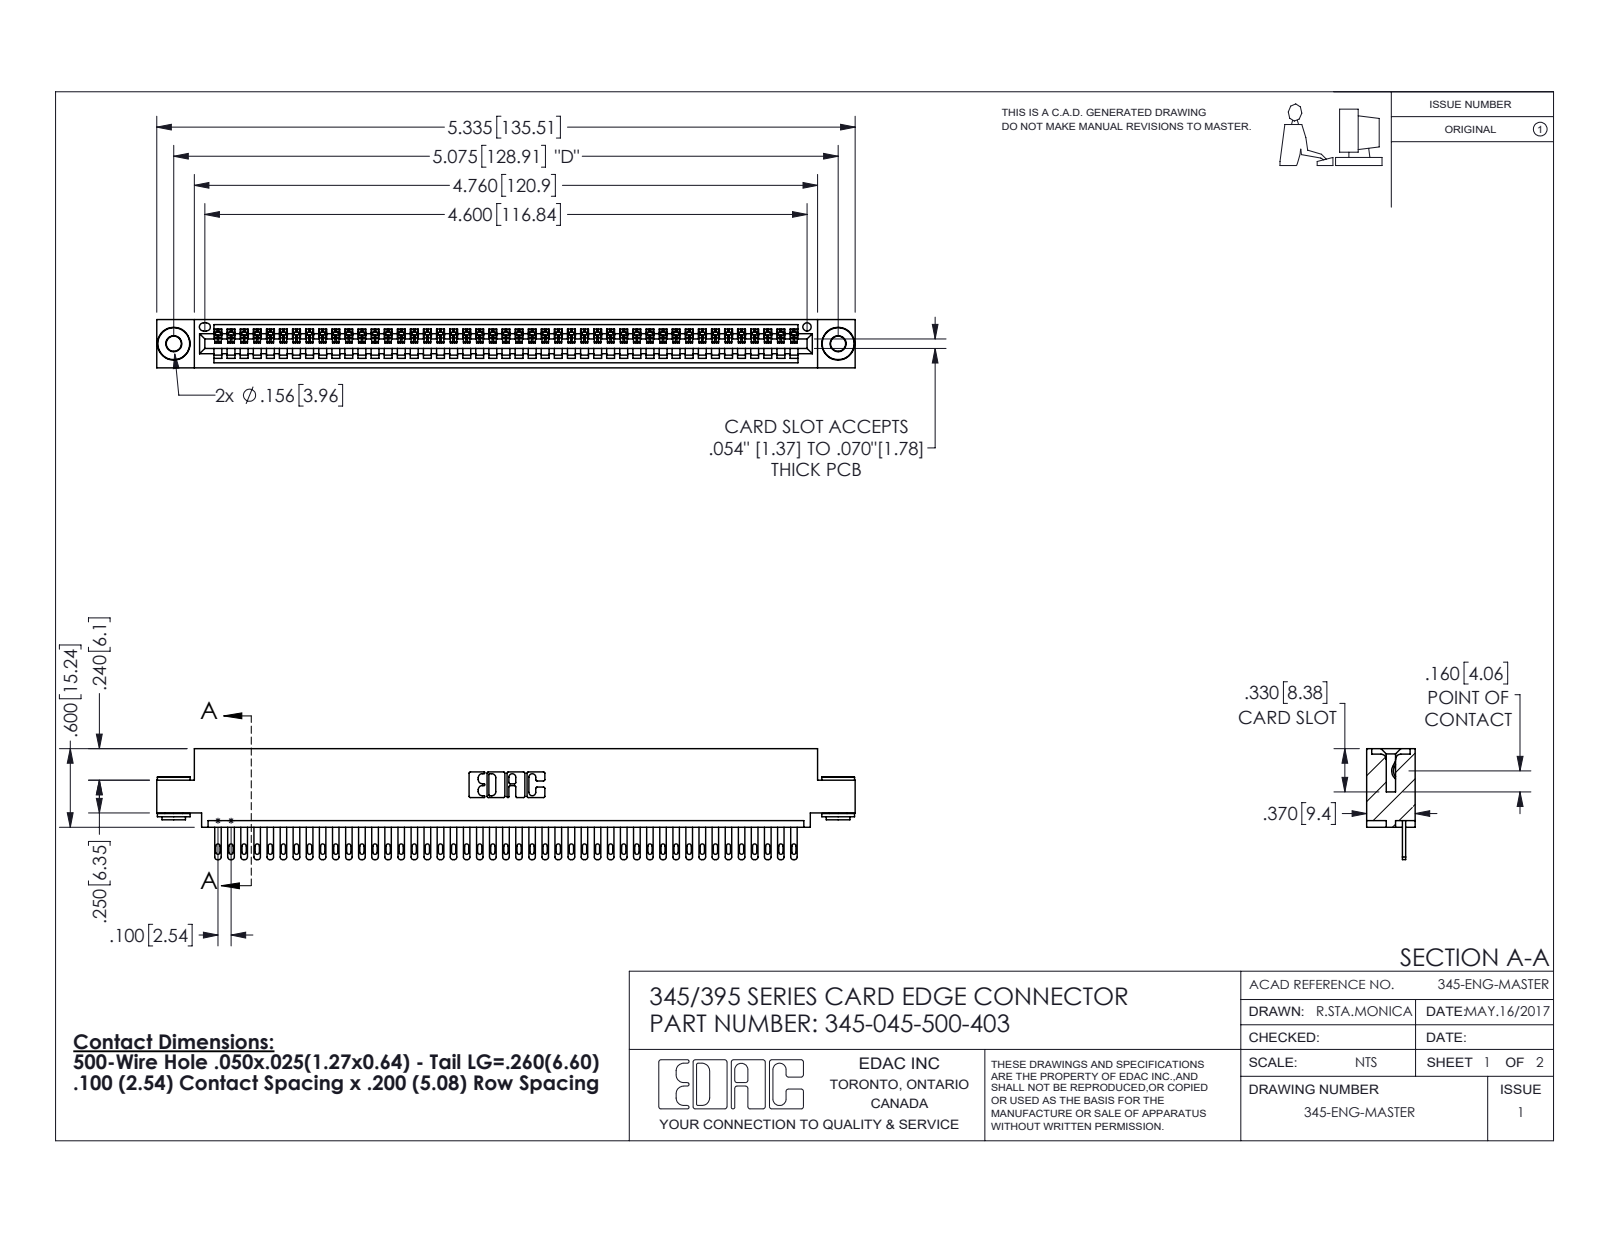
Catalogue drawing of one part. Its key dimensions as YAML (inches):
part_name: "345-292-001_345-293-100; 345-045-500-403; 345-250-002_345-250-002-102; 345 Part_0.110 Offset - 0.156 Dia-TH"
step_written_by: "SolidWorks 2016 (CONFIG_CONTROL_DESIGN)"
units: inches
bodies: {solids: 48, faces: 2598, planar: 1624, cylindrical: 966, other: 8}
overall_size: [5.335, 0.847, 0.37]
volume: 0.785
surface_area: 27.19
round_holes:
  - {diameter: 0.116, count: 2}
  - {diameter: 0.156, count: 2}
  - {diameter: 0.064, count: 1}
round_bosses_or_shafts:
  - {diameter: 0.25, count: 2}
  - {diameter: 0.18, count: 2}
  - {diameter: 0.136, count: 2}
partial_cylinders:
  - {radius: 0.006, count: 90}
  - {radius: 0.016, count: 90}
  - {radius: 0.02, count: 90}
  - {radius: 0.01, count: 22}
  - {radius: 0.007, count: 6}
  - {radius: 0.031, count: 6}
  - {radius: 0.026, count: 3}
  - {radius: 0.031, count: 2}
face_to_face_distances: [0.072, 0.298, 0.37, 0.025, 0.098, 0.272, 0.2, 0.225, 0.149, 0.072]
hole_center_spacings: [0.27, 4.839, 5.075]
